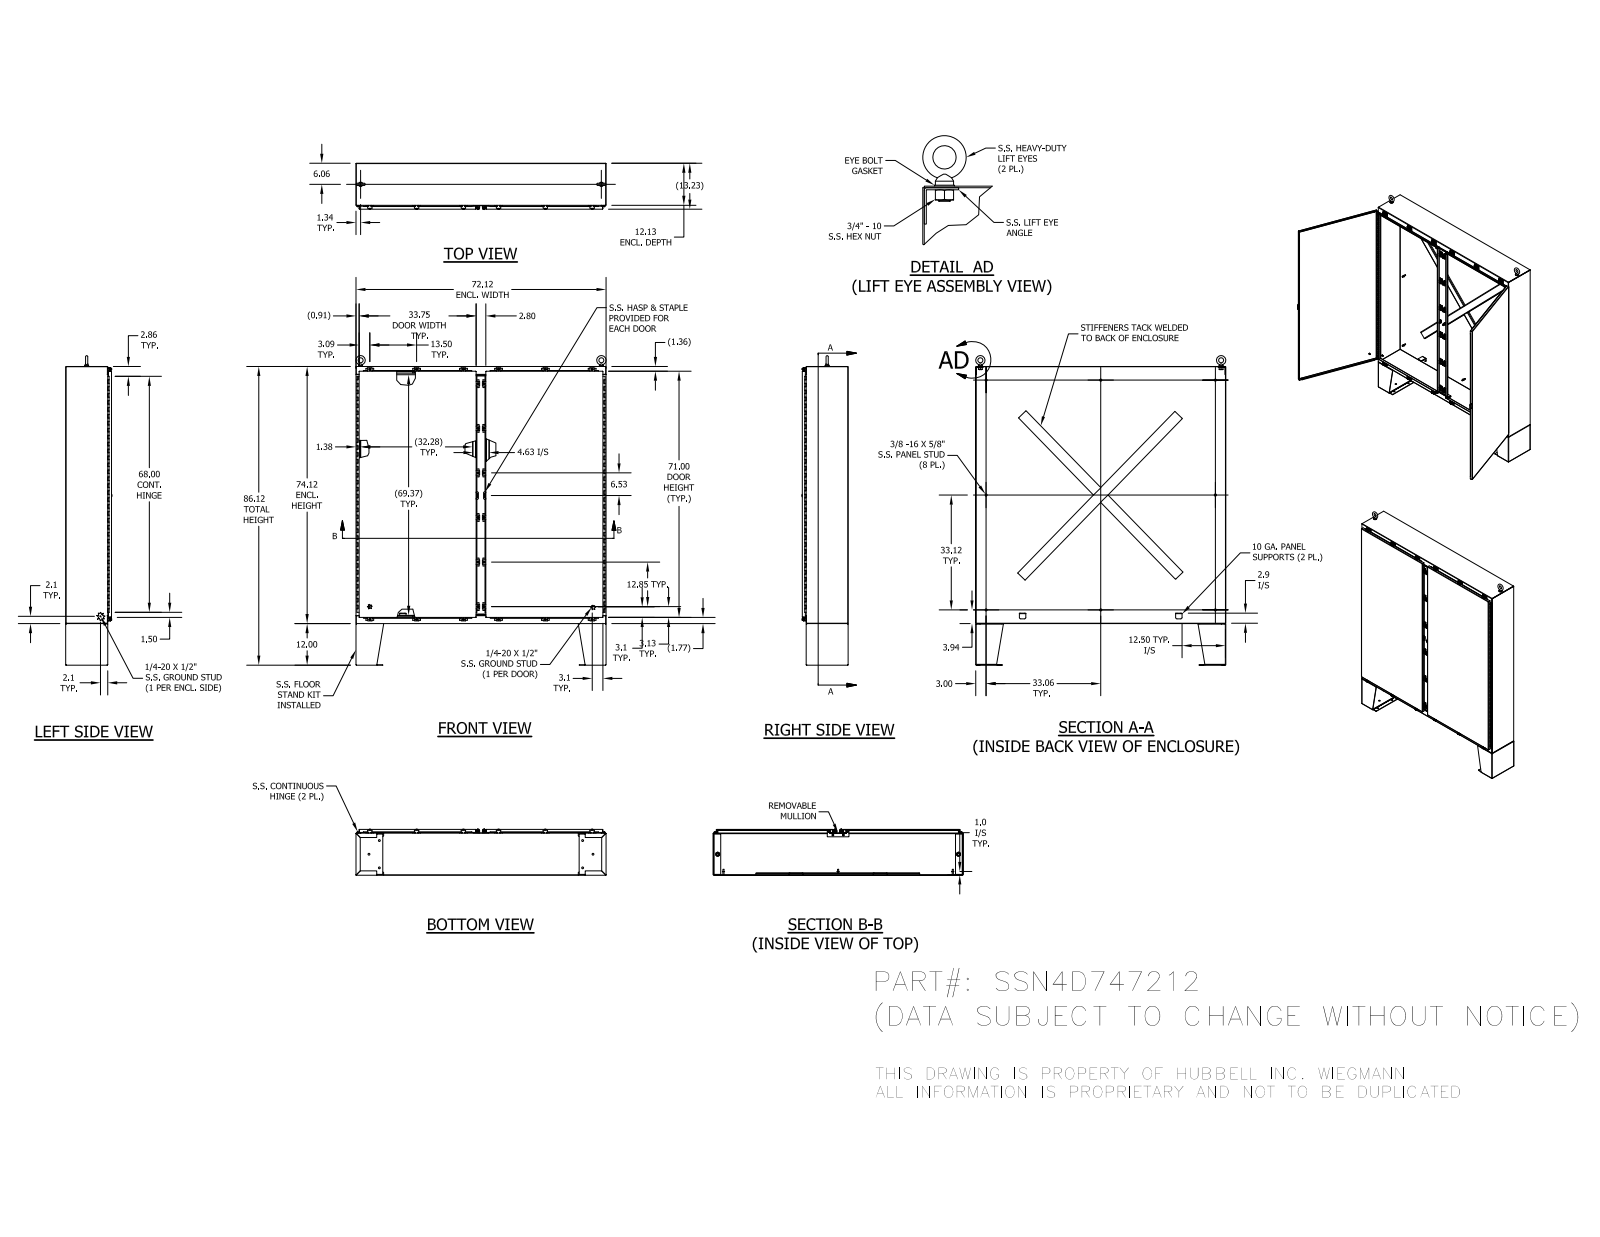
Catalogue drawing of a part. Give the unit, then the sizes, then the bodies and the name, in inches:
Units: inches
Overall size (bounding box): 89.248 × 72.125 × 13.355
Round holes (diameter × count): ⌀0.11 ×48, ⌀0.211 ×24, ⌀0.281 ×24, ⌀0.3 ×24, ⌀0.563 ×18, ⌀0.375 ×16, ⌀0.196 ×4, ⌀0.201 ×4, ⌀0.312 ×4, ⌀0.313 ×4, ⌀0.142 ×2, ⌀0.156 ×2
Round bosses / shafts (diameter × count): ⌀0.25 ×31, ⌀0.52 ×24, ⌀0.5 ×24, ⌀0.35 ×24, ⌀0.33 ×10, ⌀0.625 ×8, ⌀0.438 ×4, ⌀0.337 ×3
Partial cylindrical surfaces — rounded edges, fillets, slot ends (radius × count): R0.03 ×268, R0.125 ×62, R0.141 ×48, R0.25 ×39, R0.062 ×34, R0.031 ×24, R0.1 ×24, R0.016 ×16
Main face-to-face distances: 0.094, 13.133, 13.039, 13.227, 12.031, 1.102, 72.031, 74.031, 12.125, 1.008
Hole centre spacings: 13.5, 71.863, 72.793, 72.969, 73.269, 0.876, 0.876, 1.625
Volume: 1 664 in³ · Surface area: 35 263 in²
Bodies: 185 solids, 6996 faces (2802 planar, 2798 cylindrical, 1396 other)
Part name (STEP PRODUCT): 316298_1; 349131_1; 32912_1; 38714_1 (+8 more)
STEP written by: SolidWorks 2014 (AUTOMOTIVE_DESIGN)
